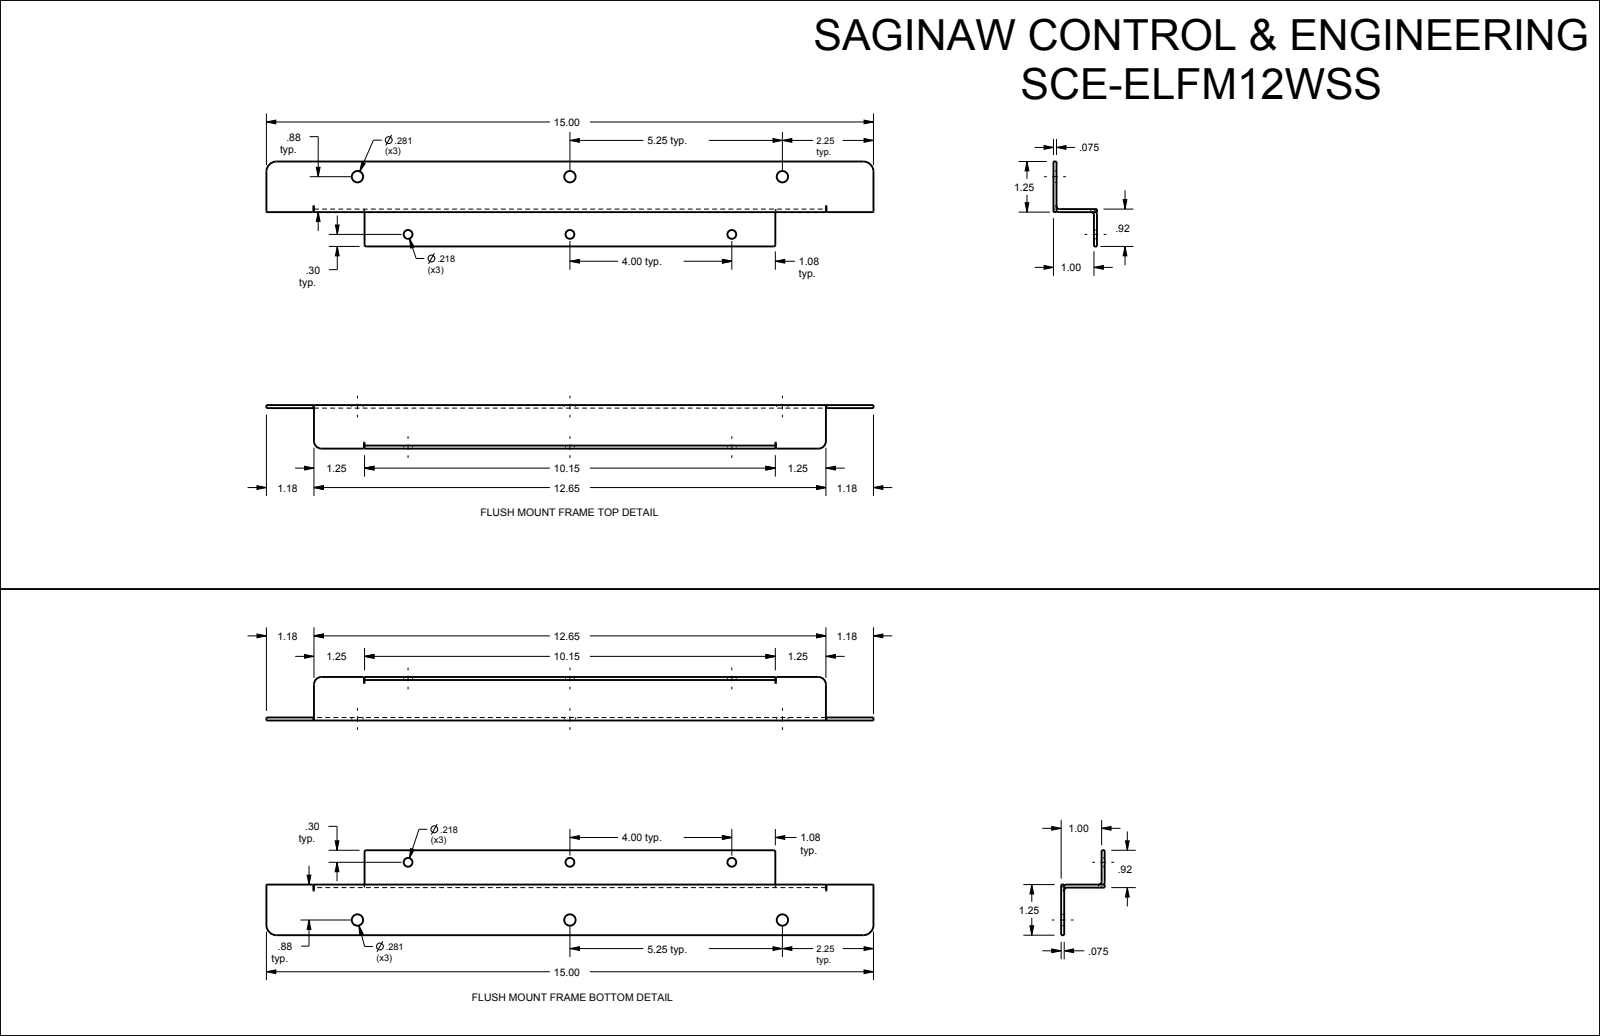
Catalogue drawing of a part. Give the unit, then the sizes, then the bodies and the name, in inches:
Units: inches
Overall size (bounding box): 15 × 14.35 × 1.075
Round holes (diameter × count): ⌀0.218 ×6, ⌀0.281 ×6
Partial cylindrical surfaces — rounded edges, fillets, slot ends (radius × count): R0.015 ×10, R0.008 ×4, R0.04 ×4, R0.051 ×4, R0.126 ×4, R0.25 ×4, R0.007 ×2, R0.187 ×2
Main face-to-face distances: 0.075, 1, 0.075, 11.925, 1.075, 0.925, 11.85, 12, 1.175, 1.25
Hole centre spacings: 4, 5.25, 9.359, 11.47, 14.578, 10.75, 13.6, 1.895
Volume: 5.817 in³ · Surface area: 161.3 in²
Bodies: 2 solids, 96 faces (44 planar, 52 cylindrical, 0 other)
Part name (STEP PRODUCT): SCE-ELFM12W
STEP written by: SolidWorks 2019 (CONFIG_CONTROL_DESIGN)
